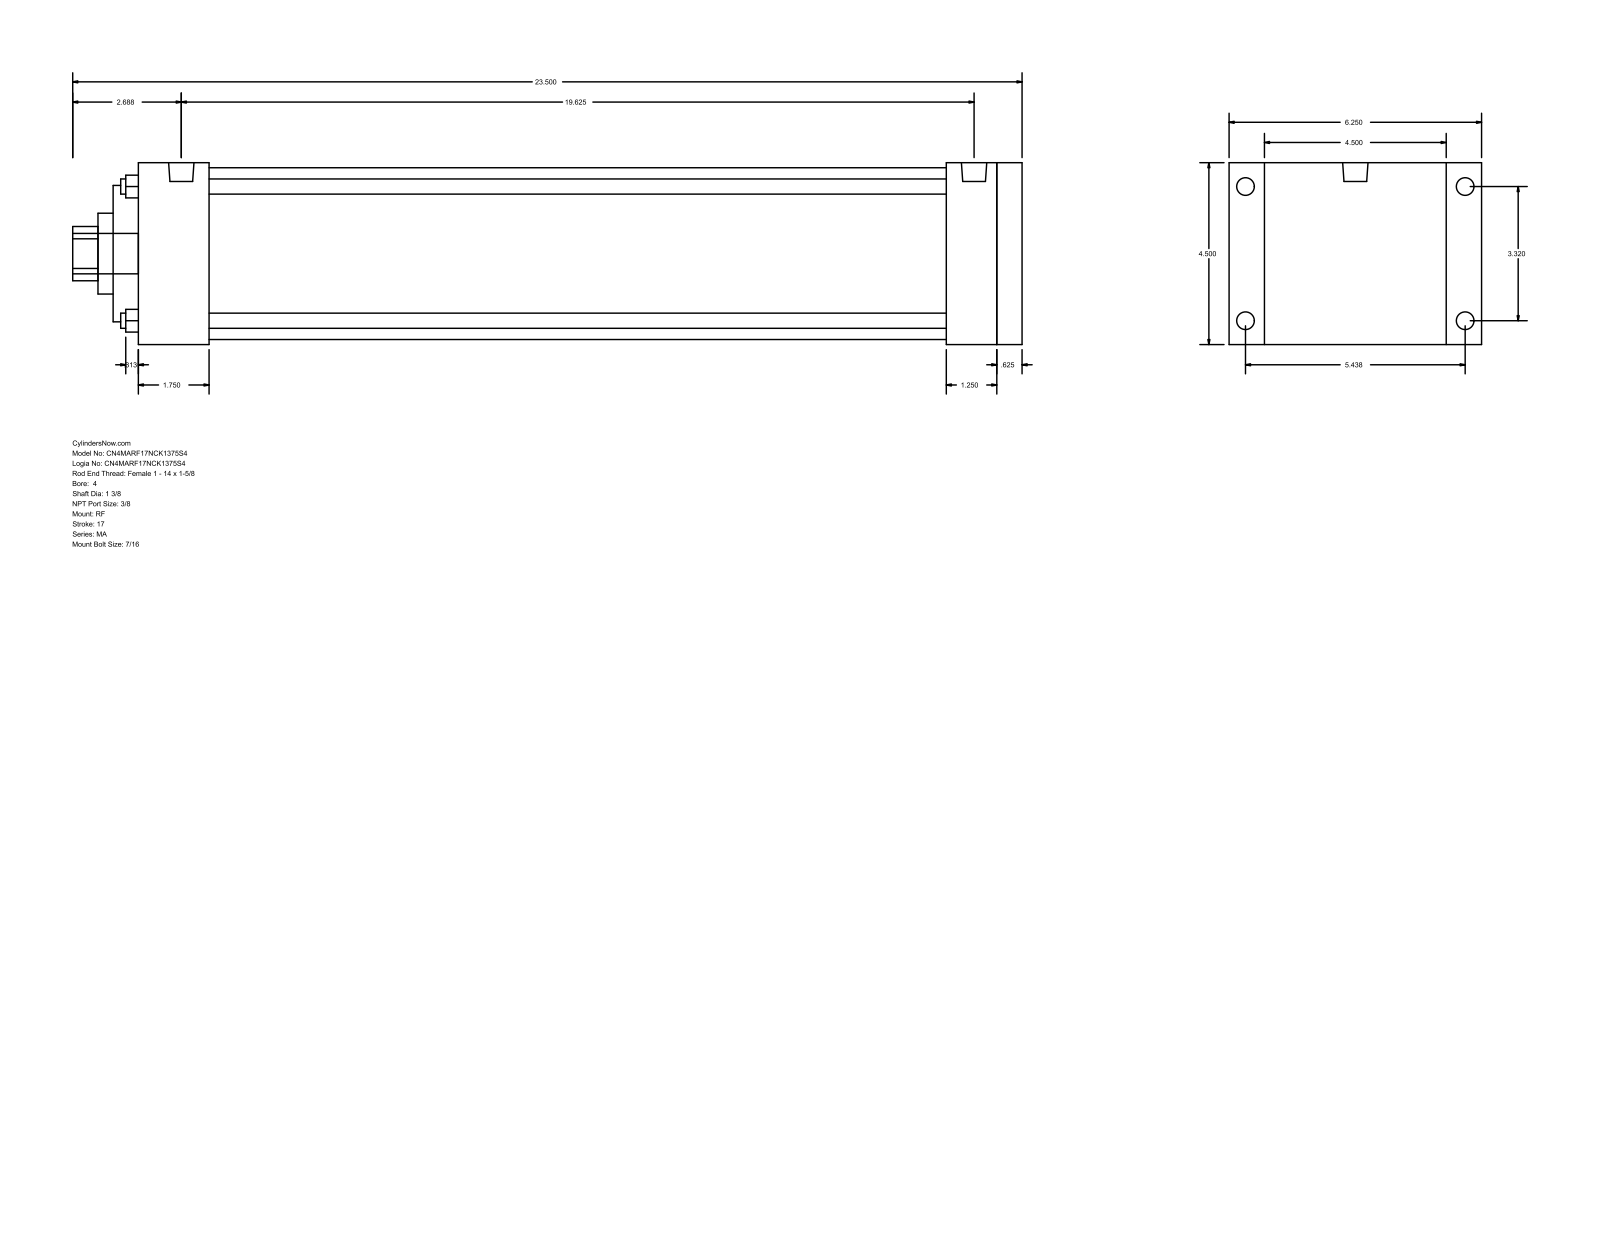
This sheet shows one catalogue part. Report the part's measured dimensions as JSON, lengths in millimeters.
{"part_name": "MA_RF__0400_1.375", "step_written_by": "GSSL Pune (CONFIG_CONTROL_DESIGN)", "units": "millimeters", "bodies": {"solids": 0, "faces": 94, "planar": 65, "cylindrical": 29, "other": 0}, "overall_size": [596.9, 158.75, 114.3], "round_holes": [[9.53, 4], [34.92, 1], [50.8, 1], [85.72, 1], [107.95, 1]], "round_bosses_or_shafts": [[11.11, 8], [15.93, 2], [25.4, 1]], "partial_cylinders_radius": [[17.06, 1]], "face_to_face_distances": [114.3, 555.63, 15.88, 539.75, 15.87, 555.62, 571.5, 22.23, 136.53, 523.87], "hole_center_spacings": [59.62, 84.32, 119.25]}
